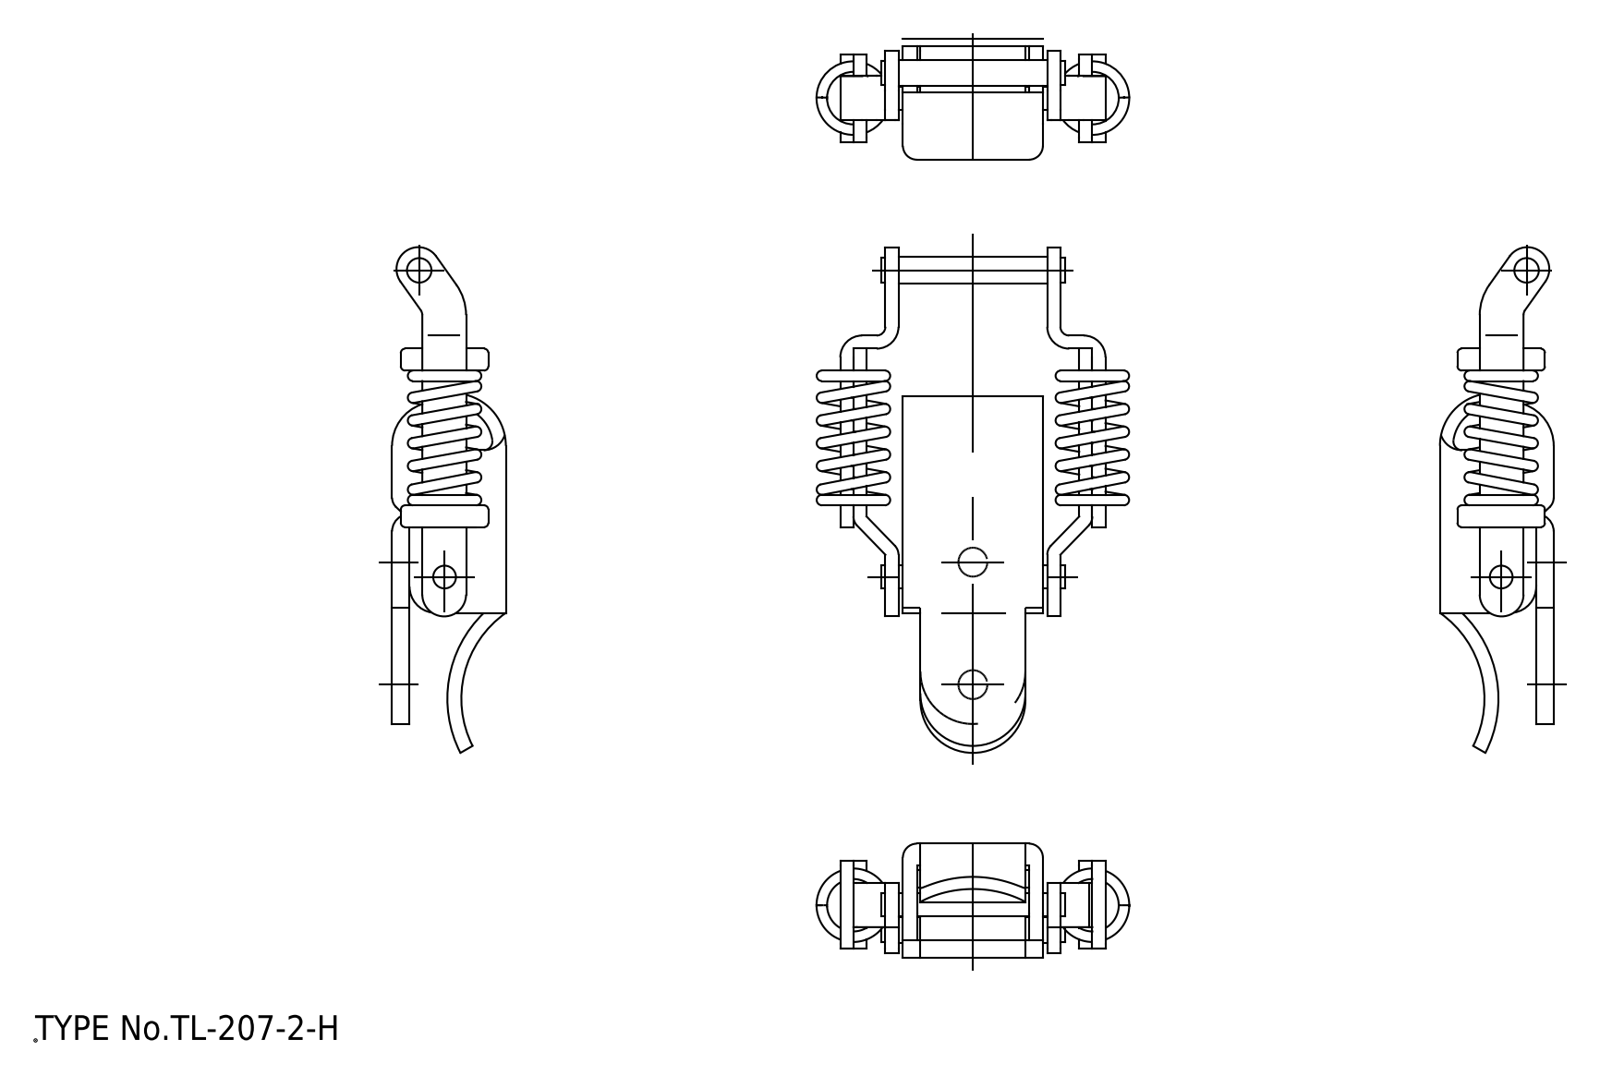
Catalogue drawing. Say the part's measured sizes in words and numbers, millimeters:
The part is named "アーム(A); アーム(B); ベース; レバー (+2 more)". Its 3-D file was written by "spGate 19.8.4 (****-****-****-****) (AUTOMOTIVE_DESIGN)". It is 6 solids with 220 faces: 114 planar, 78 cylindrical and 28 other. Overall it measures 57.8 by 35.73 by 13 millimeters. Its volume is 4 254 cubic millimeters and its surface area 6 973 square millimeters. Round holes: 2 of diameter 3.3. Round bosses or shafts: 1 of diameter 3, 1 of diameter 2.8, 1 of diameter 2.6. Partial cylindrical surfaces (rounded edges, fillets, slot ends): 9 of radius 0.5, 7 of radius 2.5, 5 of radius 1.5, 3 of radius 1, 3 of radius 6, 2 of radius 1.6, 2 of radius 2, 2 of radius 3. The main face-to-face distances are 2, 1.6, 1.5, 5.65, 21.65, 27.3, 7.25, 20.05, 14.4, 16. The hole center spacings are 14.
